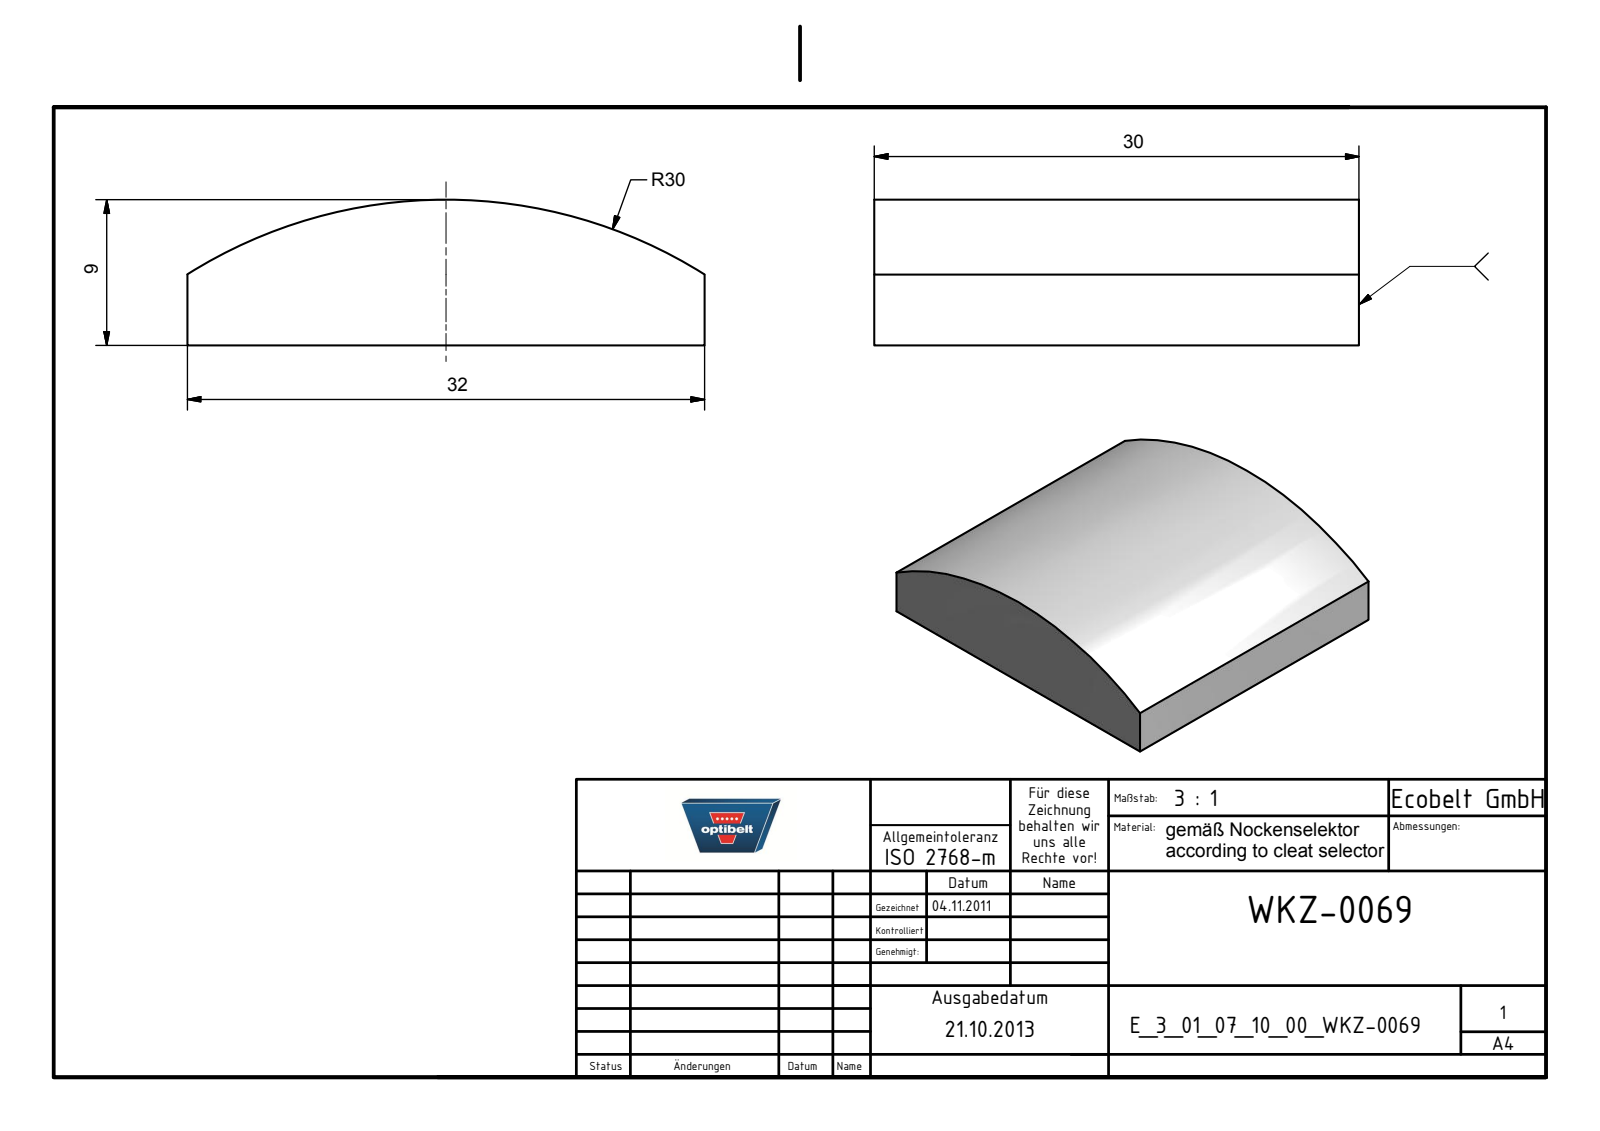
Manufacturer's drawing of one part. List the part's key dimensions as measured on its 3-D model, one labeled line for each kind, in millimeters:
Part name (STEP PRODUCT): E_3_01_07_10_00_WKZ-0069
STEP written by: Autodesk Inventor 2025 (AUTOMOTIVE_DESIGN)
Units: millimetres
Bodies: 1 solid, 6 faces (5 planar, 1 cylindrical, 0 other)
Overall size (bounding box): 32 × 30 × 9
Volume: 7 210 mm³ · Surface area: 2 716 mm²
Partial cylindrical surfaces — rounded edges, fillets, slot ends (radius × count): R30 ×1
Main face-to-face distances: 30, 32
